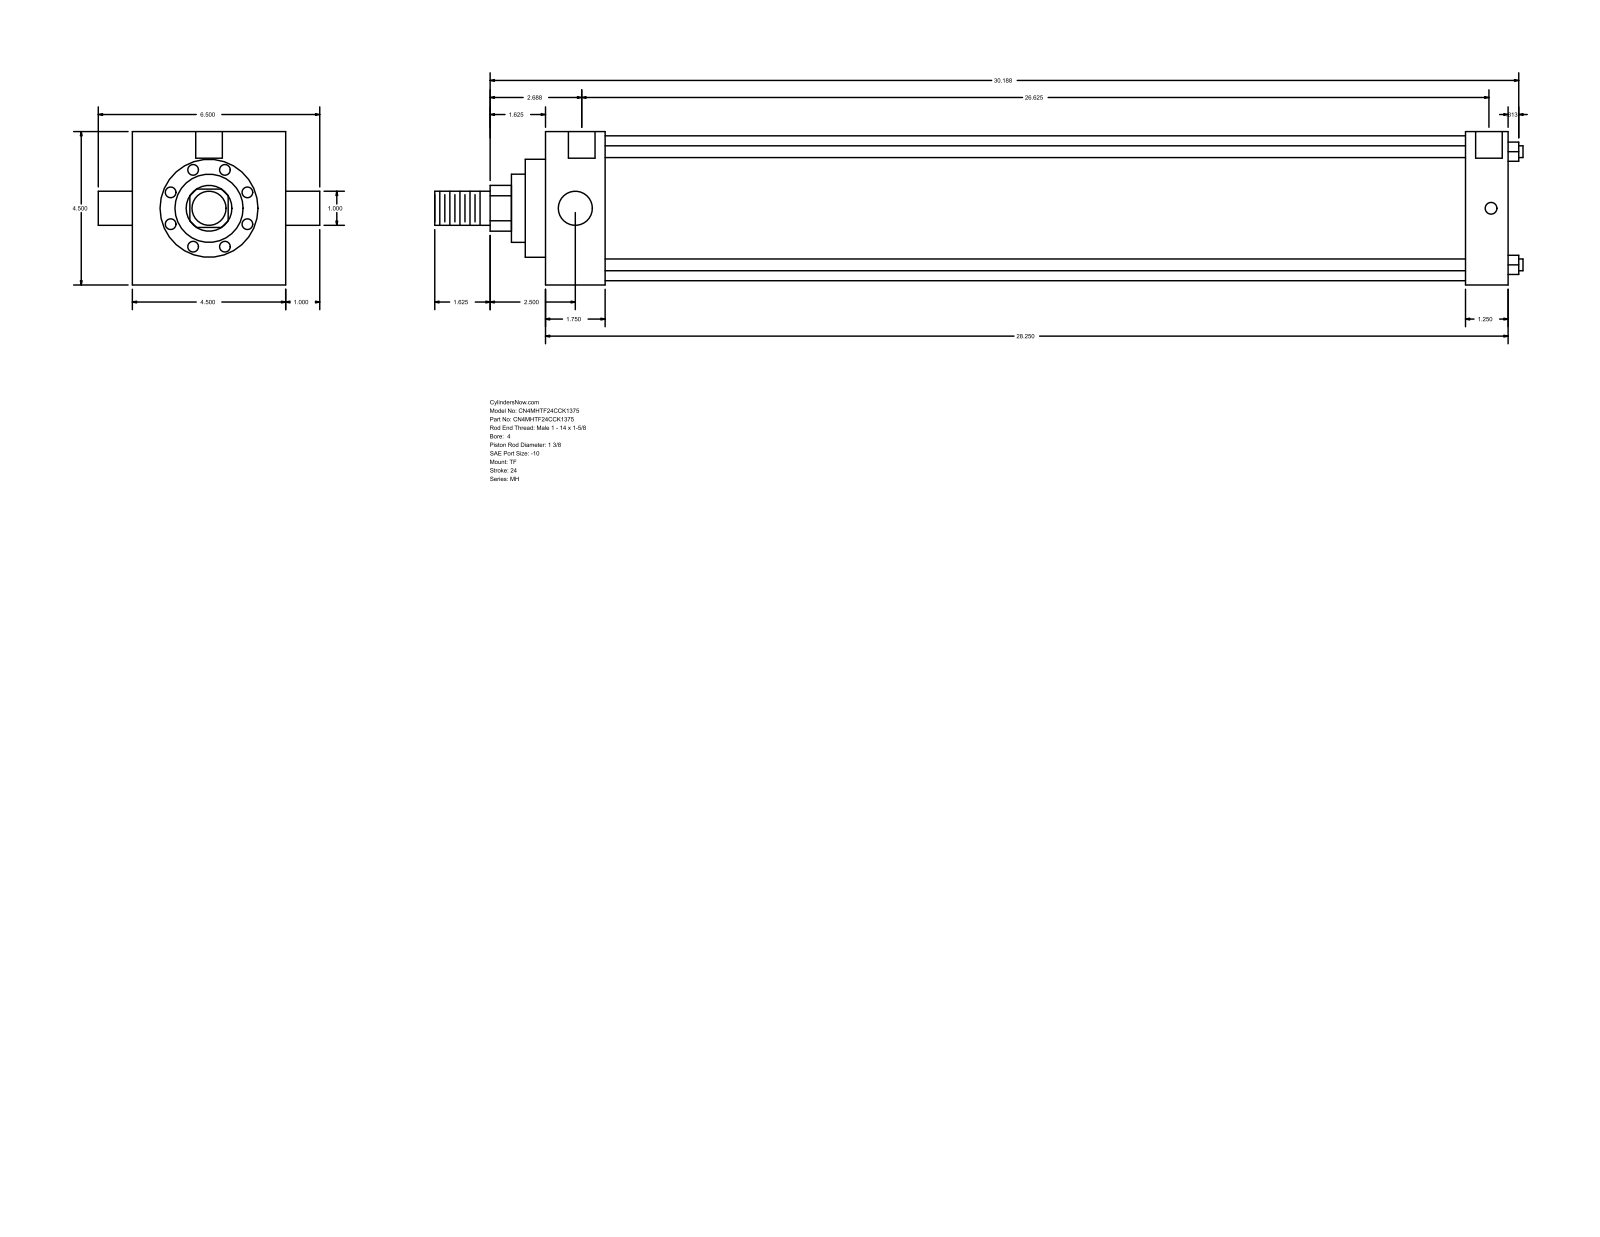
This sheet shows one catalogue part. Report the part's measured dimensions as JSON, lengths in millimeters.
{"part_name": "MH_TF__0400_1.375", "step_written_by": "GSSL Pune (CONFIG_CONTROL_DESIGN)", "units": "millimeters", "bodies": {"solids": 0, "faces": 86, "planar": 61, "cylindrical": 25, "other": 0}, "overall_size": [811.21, 165.1, 114.3], "round_holes": [[8.73, 3], [19.84, 2]], "round_bosses_or_shafts": [[8.76, 4], [25.4, 2], [107.95, 1], [73.03, 1], [50.8, 1], [34.92, 1]], "partial_cylinders_radius": [[17.06, 1]], "face_to_face_distances": [114.3, 717.56, 44.45, 673.11, 685.81, 641.36, 31.75, 15.08, 59.53, 700.89], "hole_center_spacings": [1.58, 1.59, 676.28, 677.86, 677.87, 679.45]}
